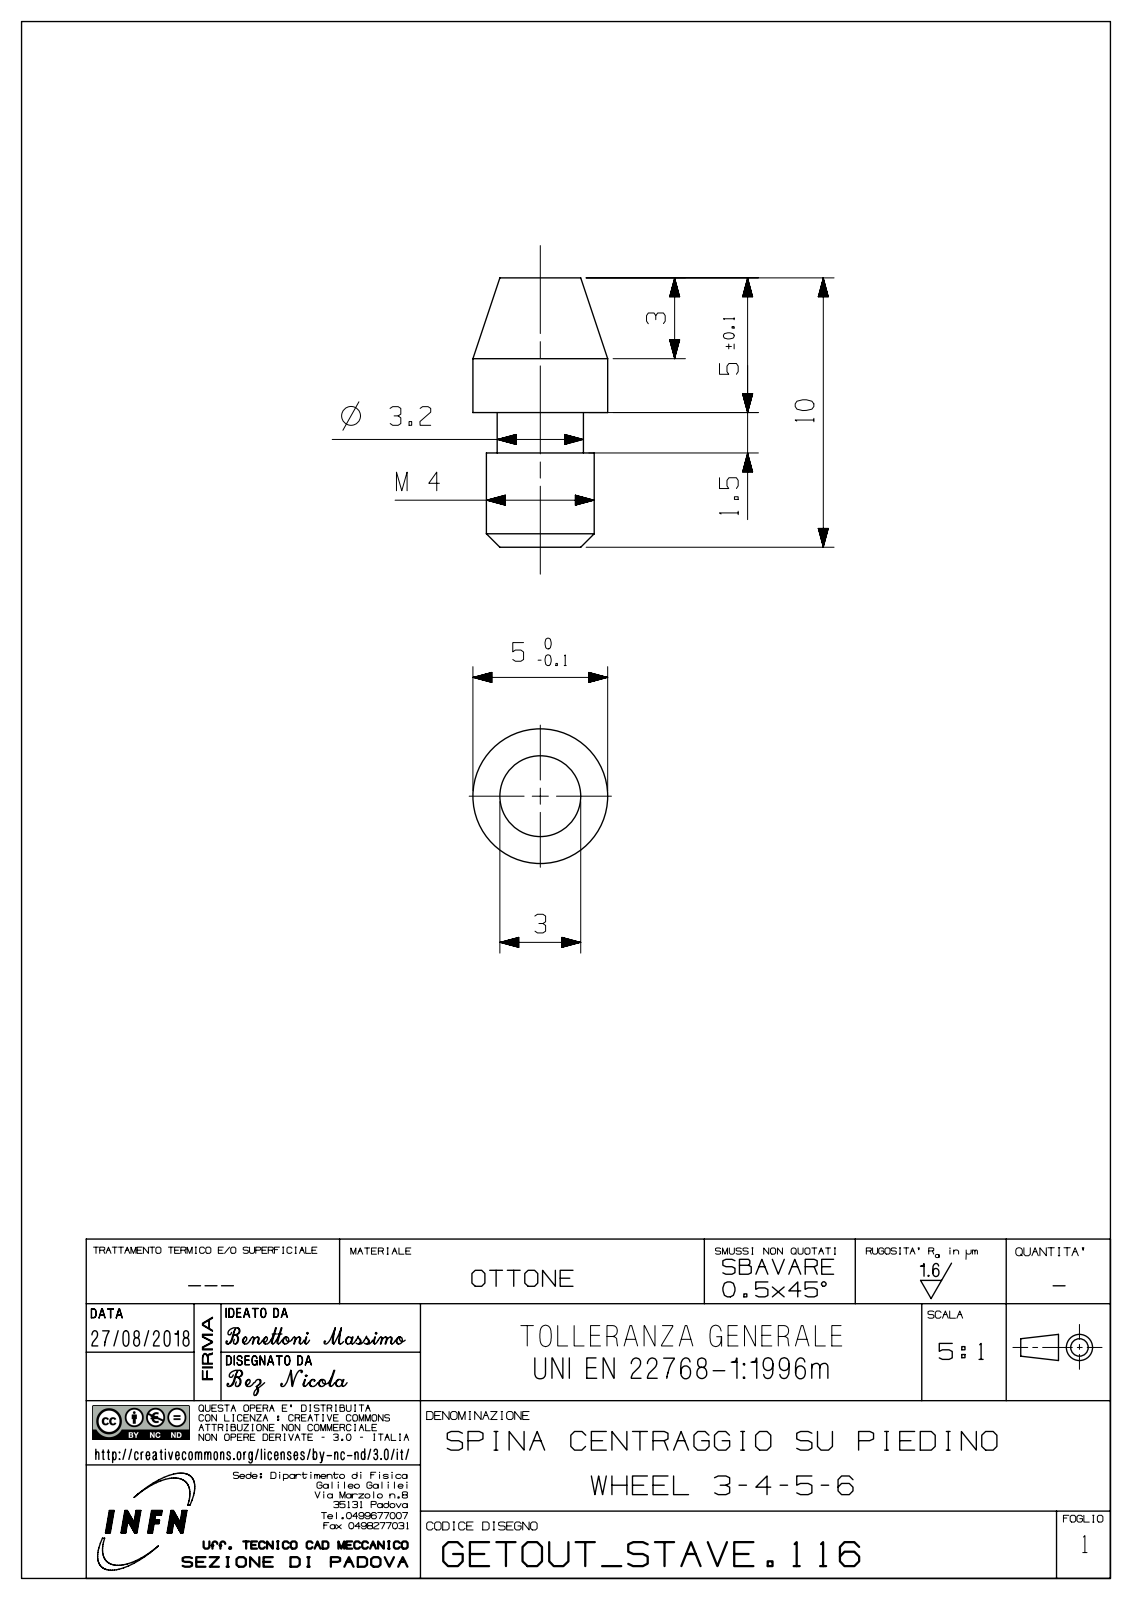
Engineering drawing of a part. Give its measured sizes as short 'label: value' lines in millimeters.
name: bez8324385A6v0x
written by: SIEMENS PLM Software NX 12.0 (AUTOMOTIVE_DESIGN)
unit: mm
bodies: 1 solid, 9 faces (4 planar, 3 cylindrical, 2 other)
size: 10 × 5 × 5
volume: 132 mm³; area: 162 mm²
bosses: 1× ⌀5, 1× ⌀4, 1× ⌀3.2
face distances: 5, 10, 3.5, 1.5, 6.5
